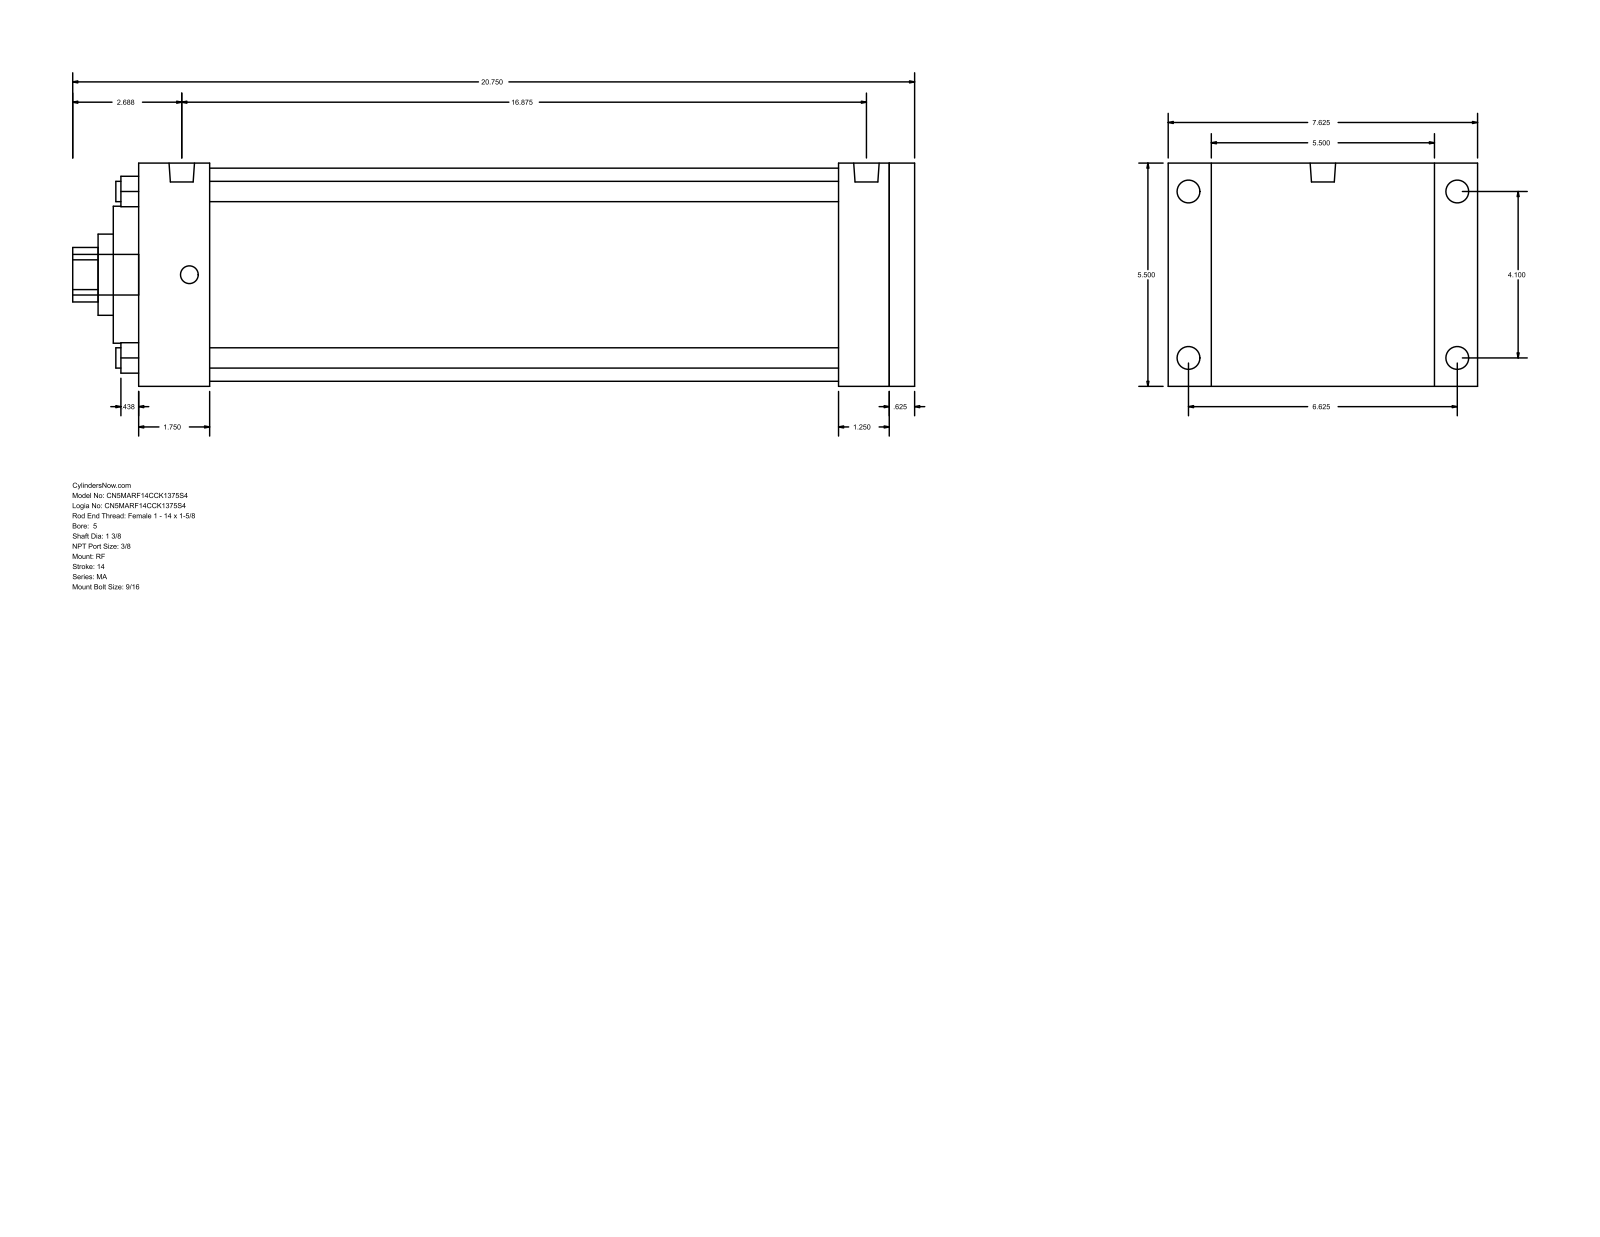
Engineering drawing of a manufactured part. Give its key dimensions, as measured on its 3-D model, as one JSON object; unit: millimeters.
{"part_name": "MA_RF__0500_1.375", "step_written_by": "GSSL Pune (CONFIG_CONTROL_DESIGN)", "units": "millimeters", "bodies": {"solids": 0, "faces": 94, "planar": 65, "cylindrical": 29, "other": 0}, "overall_size": [527.05, 193.68, 139.7], "round_holes": [[12.7, 4], [34.92, 1], [50.8, 1], [85.72, 1], [133.35, 1]], "round_bosses_or_shafts": [[14.29, 4], [11.11, 4], [15.93, 2], [25.4, 1]], "partial_cylinders_radius": [[17.06, 1]], "face_to_face_distances": [139.7, 485.78, 15.87, 469.91, 44.45, 425.46, 441.33, 438.16, 393.71, 31.75], "hole_center_spacings": [73.64, 104.14, 147.28]}
